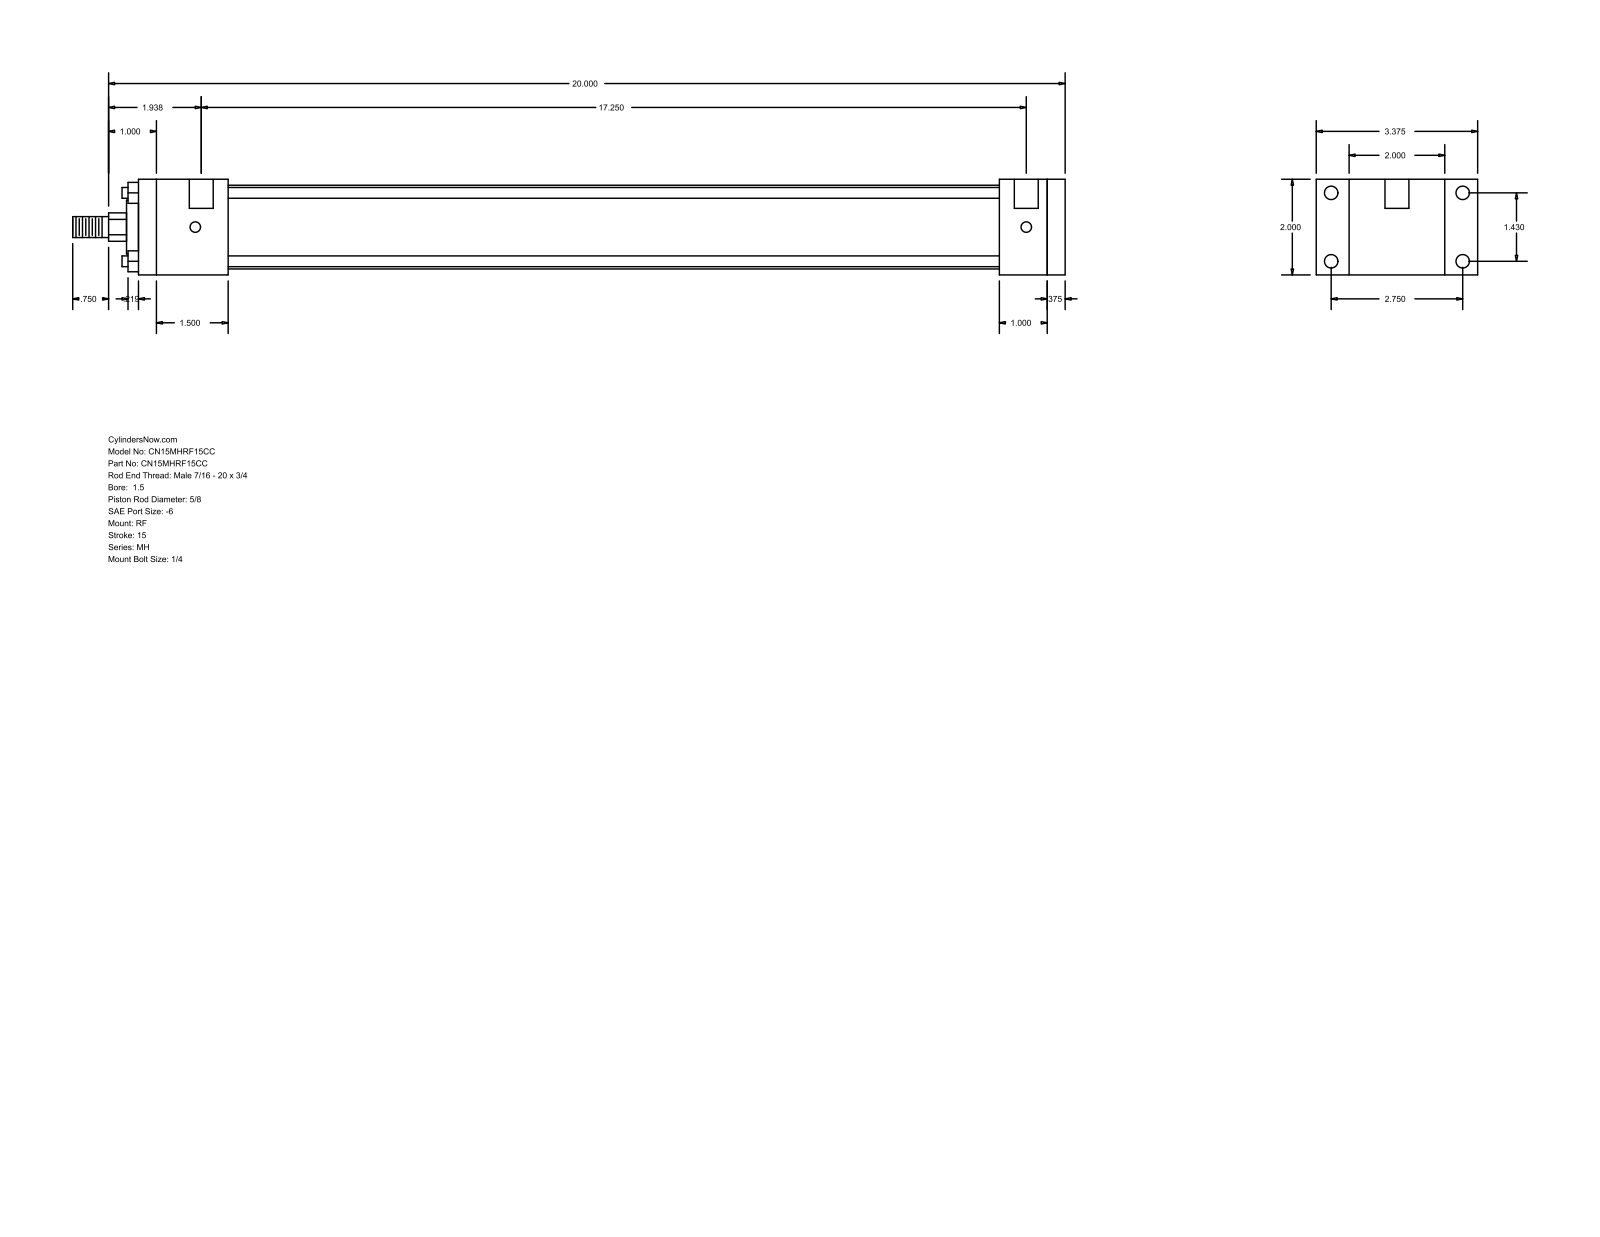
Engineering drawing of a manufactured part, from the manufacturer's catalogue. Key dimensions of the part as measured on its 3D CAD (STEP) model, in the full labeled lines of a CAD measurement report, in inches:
Part name (STEP PRODUCT): MH_RF__0150_0.625
STEP written by: GSSL Pune (CONFIG_CONTROL_DESIGN)
Units: inches
Bodies: 0 solids, 92 faces (64 planar, 28 cylindrical, 0 other)
Overall size (bounding box): 20.75 × 3.375 × 2
Round holes (diameter × count): ⌀0.219 ×4, ⌀0.281 ×4, ⌀0.5 ×2
Round bosses / shafts (diameter × count): ⌀0.225 ×4, ⌀1.75 ×1, ⌀1.125 ×1, ⌀0.625 ×1, ⌀0.437 ×1
Partial cylindrical surfaces — rounded edges, fillets, slot ends (radius × count): R0.297 ×1
Main face-to-face distances: 2, 0.375, 19.375, 19, 1.375, 0.687, 2.687, 18, 1, 1.875
Hole centre spacings: 1.43, 2.75, 3.099, 17.375, 0.125, 17.25
